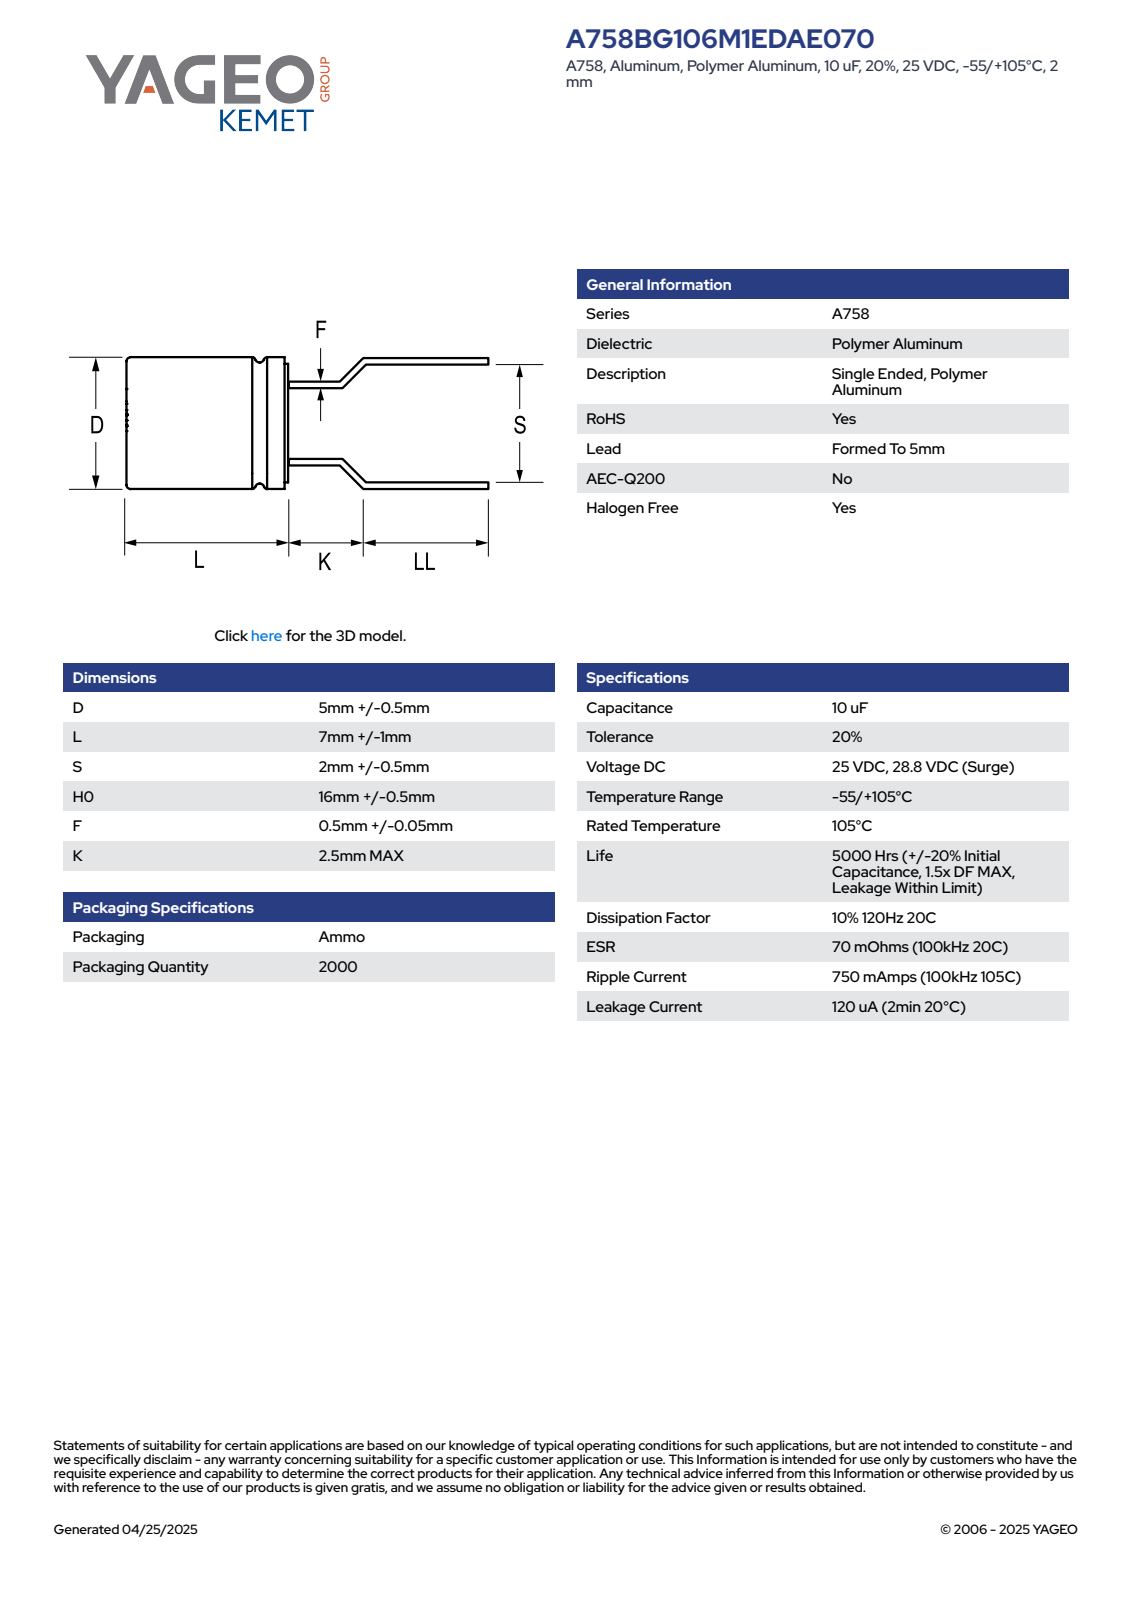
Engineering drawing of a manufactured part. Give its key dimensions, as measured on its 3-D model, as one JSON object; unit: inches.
{"part_name": "CAR_KPF_5X7_D5.5L8S2LL3F0.55K2.5", "step_written_by": "SolidWorks 2014 (AUTOMOTIVE_DESIGN)", "units": "inches", "bodies": {"solids": 4, "faces": 90, "planar": 62, "cylindrical": 18, "other": 10}, "overall_size": [0.532, 0.217, 0.217], "volume_in3": 0.012, "surface_area_in2": 0.321, "round_bosses_or_shafts": [[0.022, 6], [0.217, 1], [0.191, 1]], "face_to_face_distances": [0.315, 0.309, 0.309, 0.315, 0.532, 0.531, 0.222, 0.217, 0.02, 0.018]}
